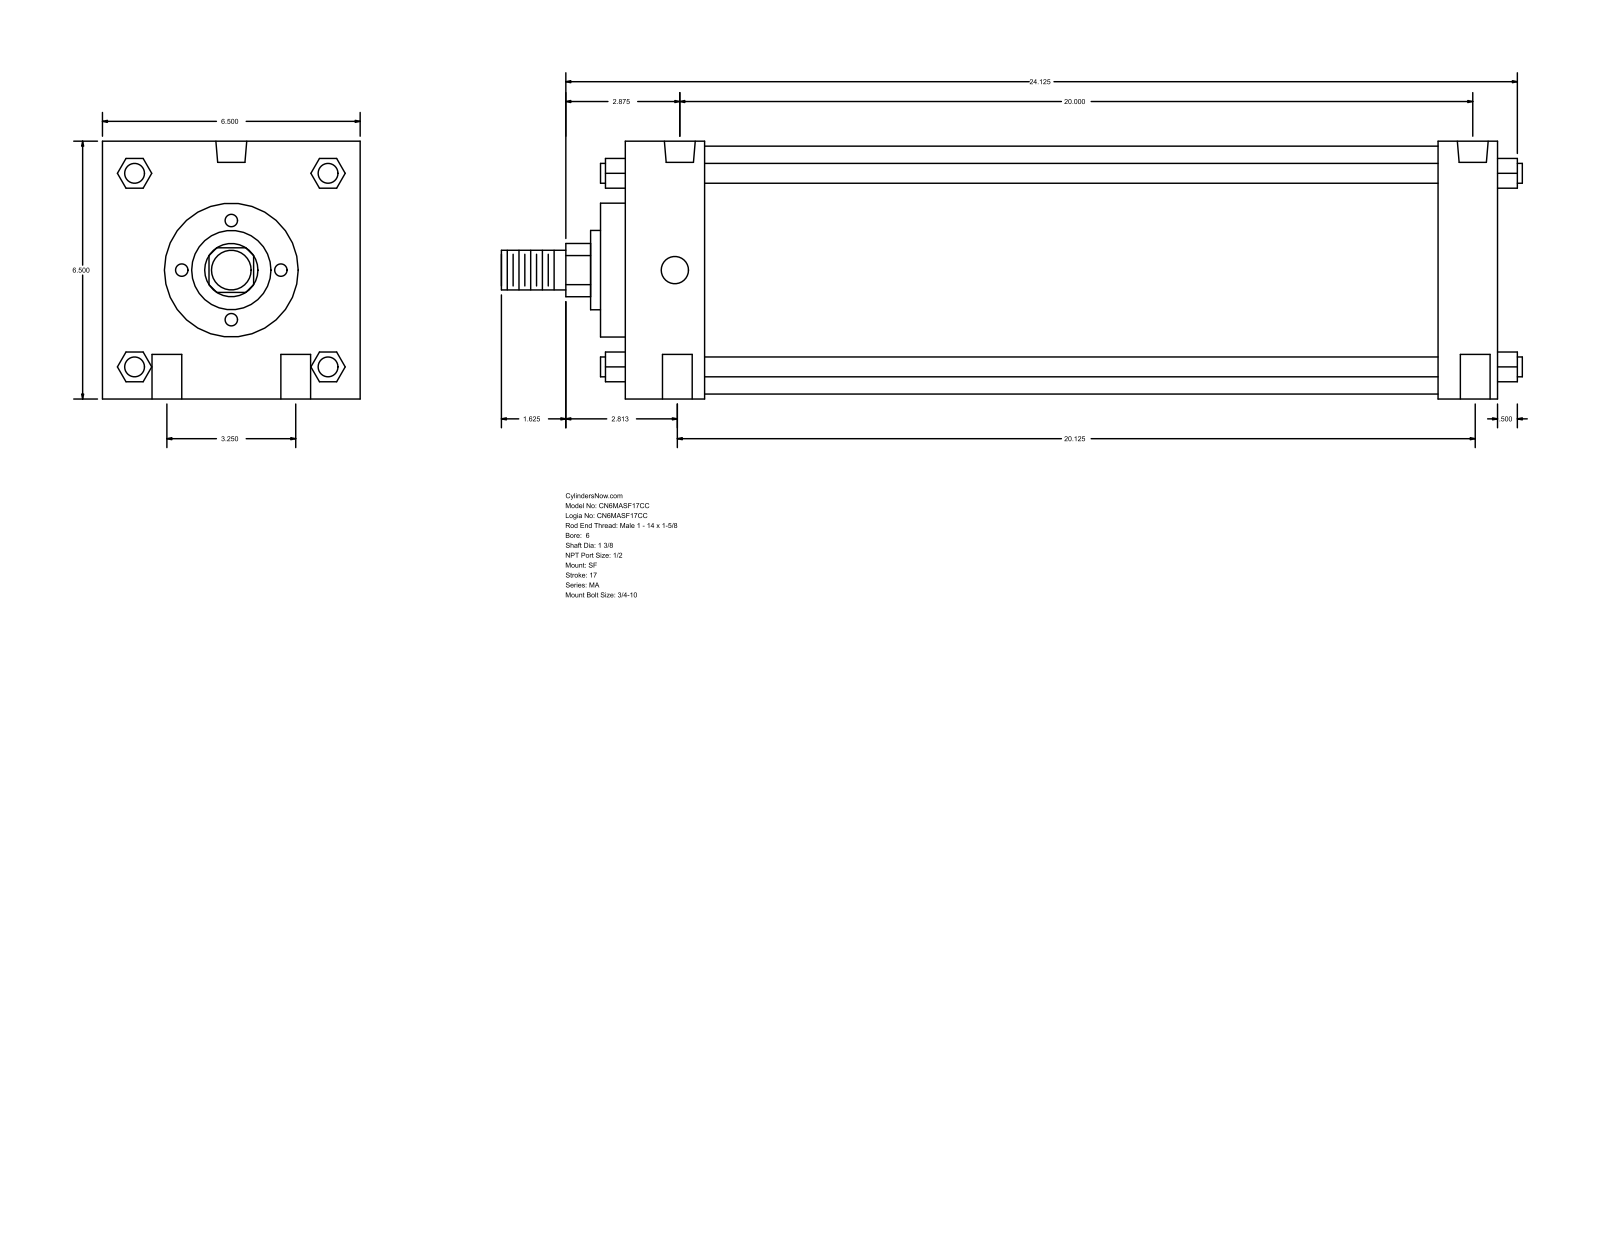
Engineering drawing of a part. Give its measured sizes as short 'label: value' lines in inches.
name: MA_SF__0600_1.375
written by: GSSL Pune (CONFIG_CONTROL_DESIGN)
unit: in
bodies: 0 solids, 126 faces (95 planar, 31 cylindrical, 0 other)
size: 25.75 × 6.5 × 6.5
holes: 4× ⌀0.75, 2× ⌀0.687, 2× ⌀0.778
bosses: 4× ⌀0.5, 1× ⌀6.25, 1× ⌀3.375, 1× ⌀2, 1× ⌀1.375, 1× ⌀1
rounds: 1× R0.672
face distances: 6.5, 22, 20.5, 2, 1.5, 18.5, 20, 2.625, 0.625, 22.625
hole spacings: 1.626, 20.128, 3.25, 20.125, 20.385, 20, 20
